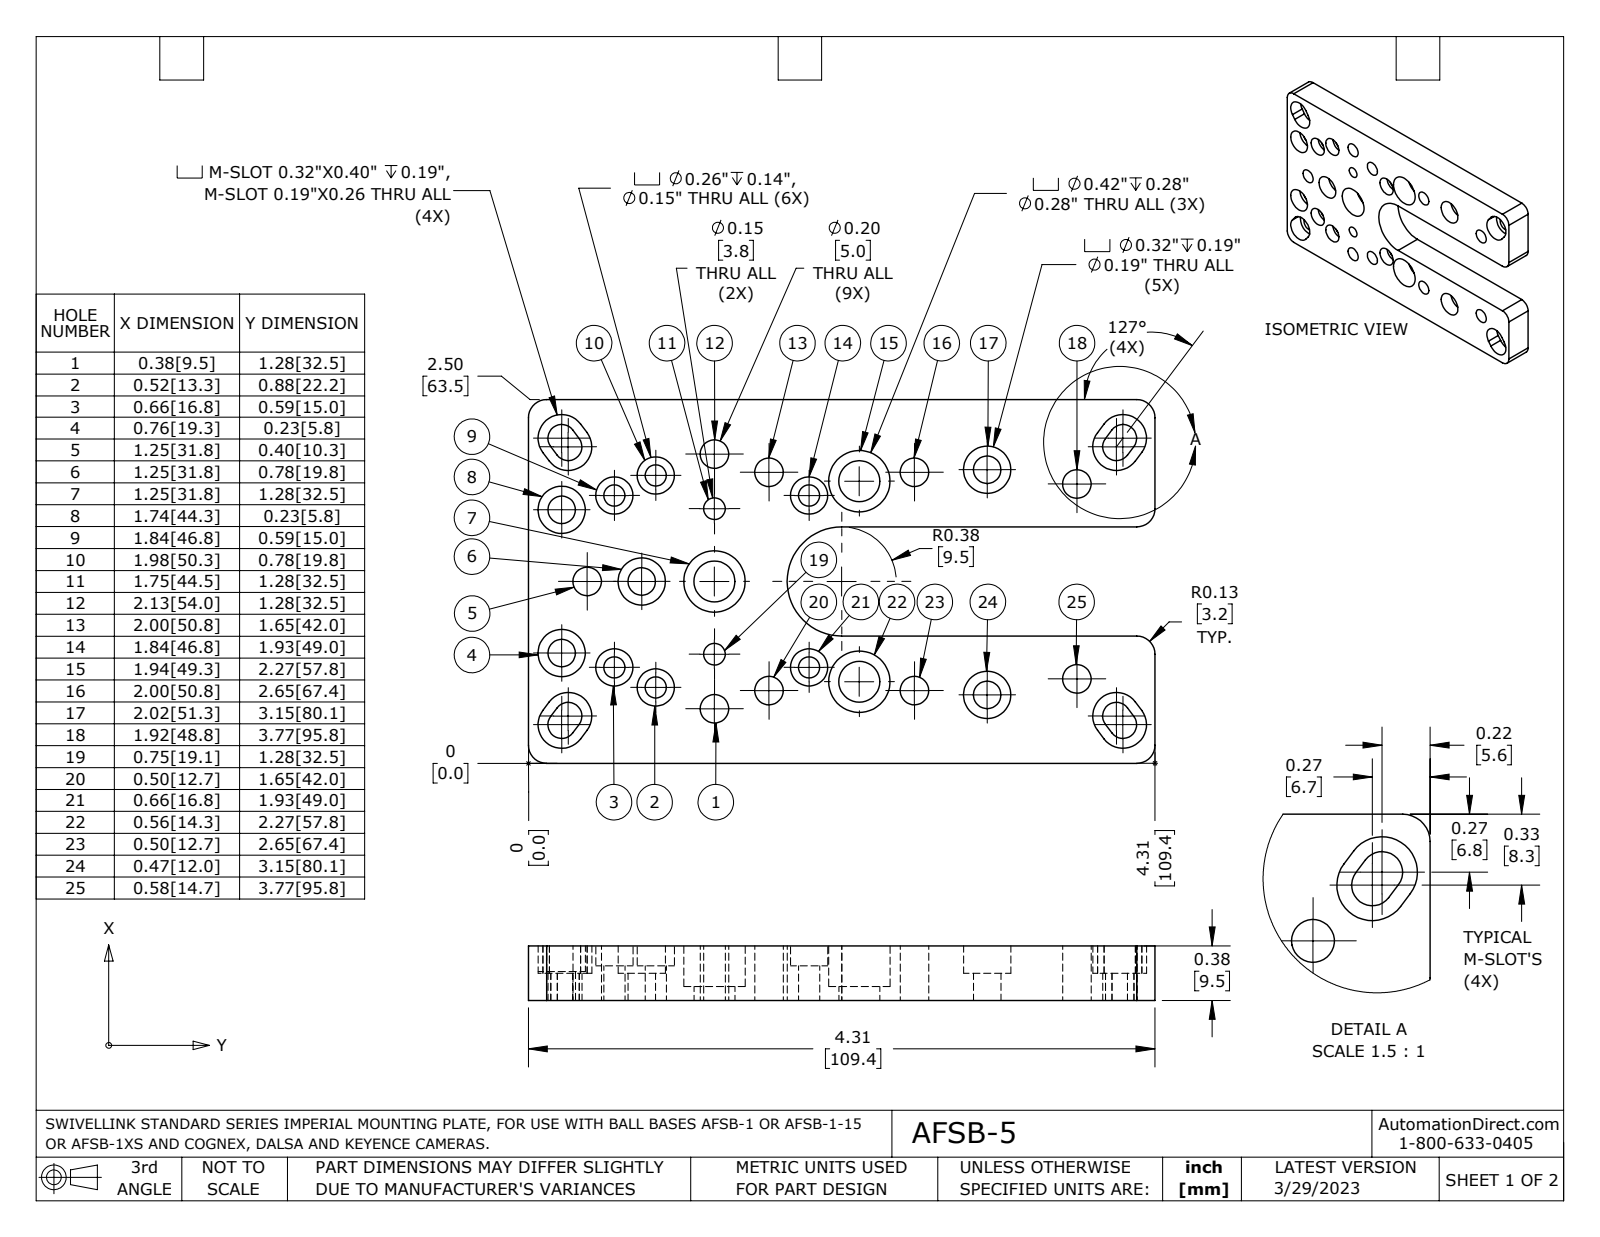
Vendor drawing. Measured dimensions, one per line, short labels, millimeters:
name: AFSB-5
written by: SolidWorks 2021 (AUTOMOTIVE_DESIGN)
unit: mm
bodies: 1 solid, 105 faces (43 planar, 62 cylindrical, 0 other)
size: 109.4 × 63.5 × 9.5
volume: 46 050 mm³; area: 19 890 mm²
holes: 9× ⌀5, 6× ⌀3.7, 6× ⌀6.5, 5× ⌀4.8, 5× ⌀8.3, 3× ⌀7.1, 3× ⌀10.7, 2× ⌀3.8
rounds: 8× R2.4, 8× R4.1, 6× R3.2, 1× R9.5
face distances: 9.5, 22.2, 41.3, 63.5, 19.1, 109.4, 4.8, 4.7, 7.1, 2.3
hole spacings: 9.5, 25.6, 12.7, 22.2, 25.4, 38.1, 8, 8.1
